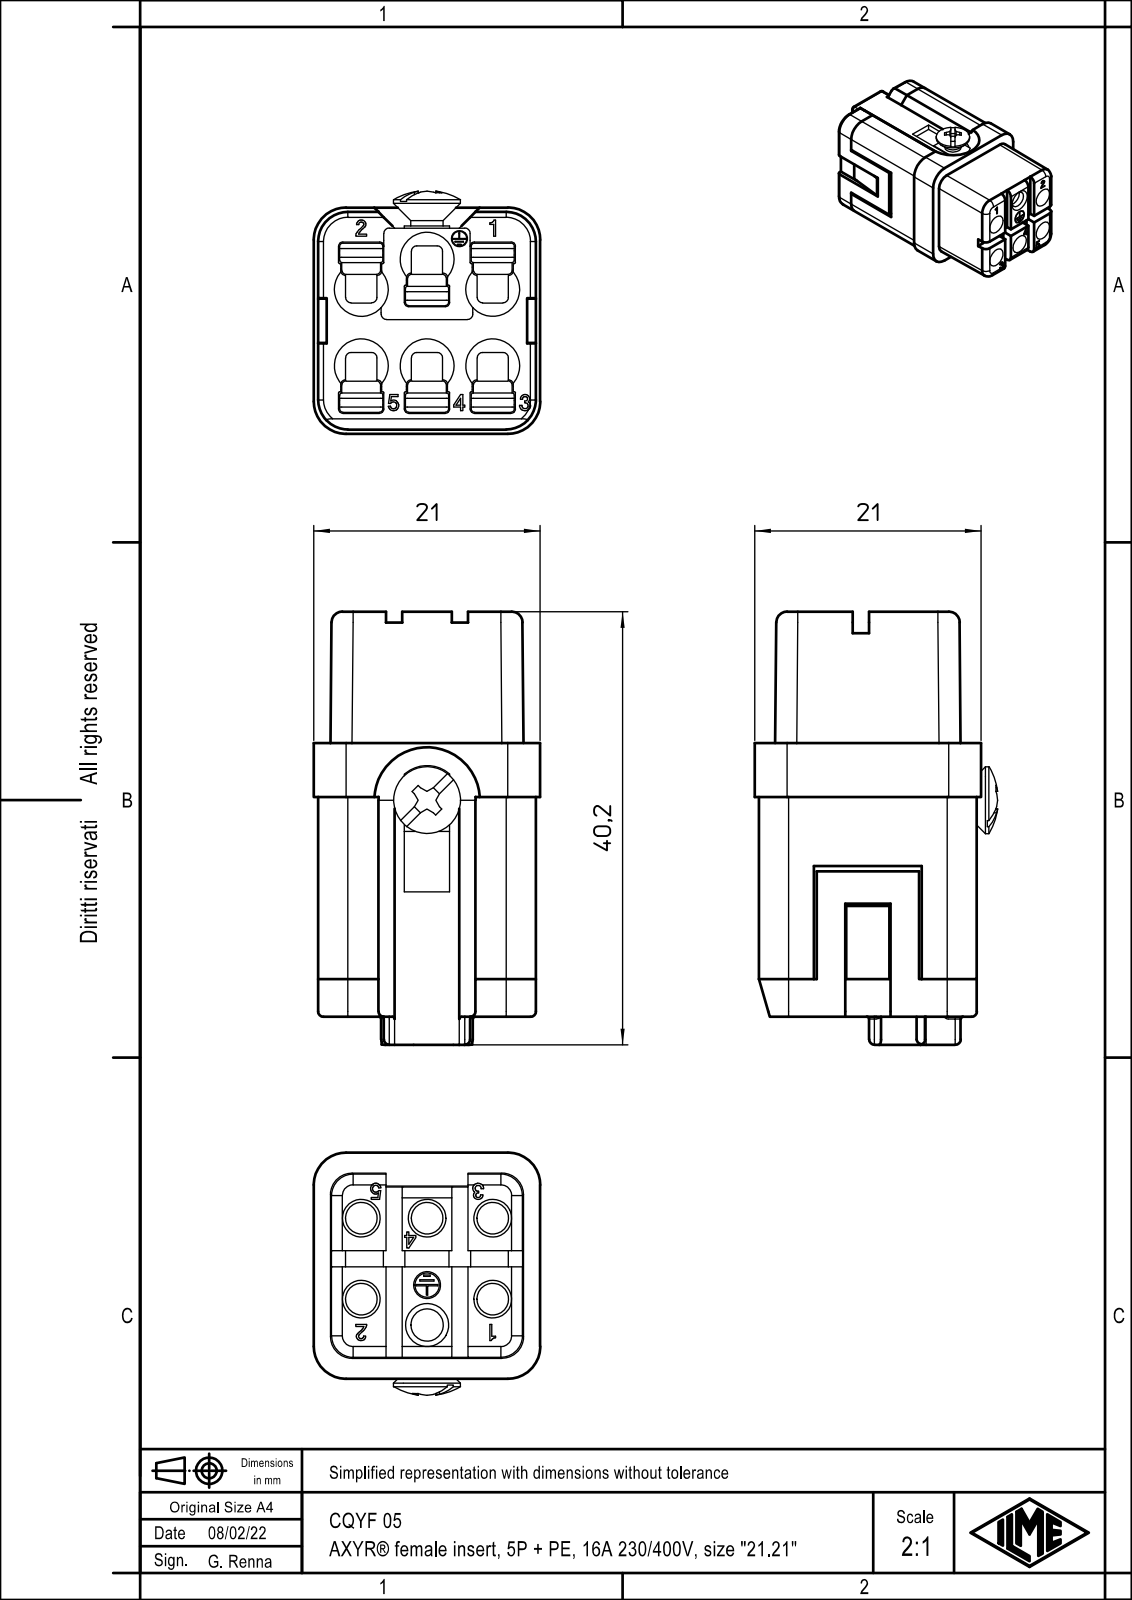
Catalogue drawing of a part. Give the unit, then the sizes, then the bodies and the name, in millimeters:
Units: millimetres
Overall size (bounding box): 40.2 × 22.52 × 21
Round holes (diameter × count): ⌀2.5 ×1, ⌀3 ×1
Round bosses / shafts (diameter × count): ⌀6.2 ×1, ⌀3 ×1, ⌀2.26 ×1
Partial cylindrical surfaces — rounded edges, fillets, slot ends (radius × count): R0.2 ×52, R0.4 ×36, R0.5 ×26, R0.1 ×12, R0.3 ×12, R2 ×7, R2.5 ×6, R1 ×5
Main face-to-face distances: 1.5, 8.7, 20.2, 0.4, 10.2, 20.6, 1.9, 10, 7.2, 18.7
Hole centre spacings: 3.7
Volume: 12 156 mm³ · Surface area: 6 464 mm²
Bodies: 1 solid, 880 faces (546 planar, 233 cylindrical, 101 other)
Part name (STEP PRODUCT): CQYF_05
STEP written by: Creo Elements/Direct Modeling 20.1B 02-Apr-2019 (C) Parametric Technology GmbH (AUTOMOTIVE_DESIGN)
